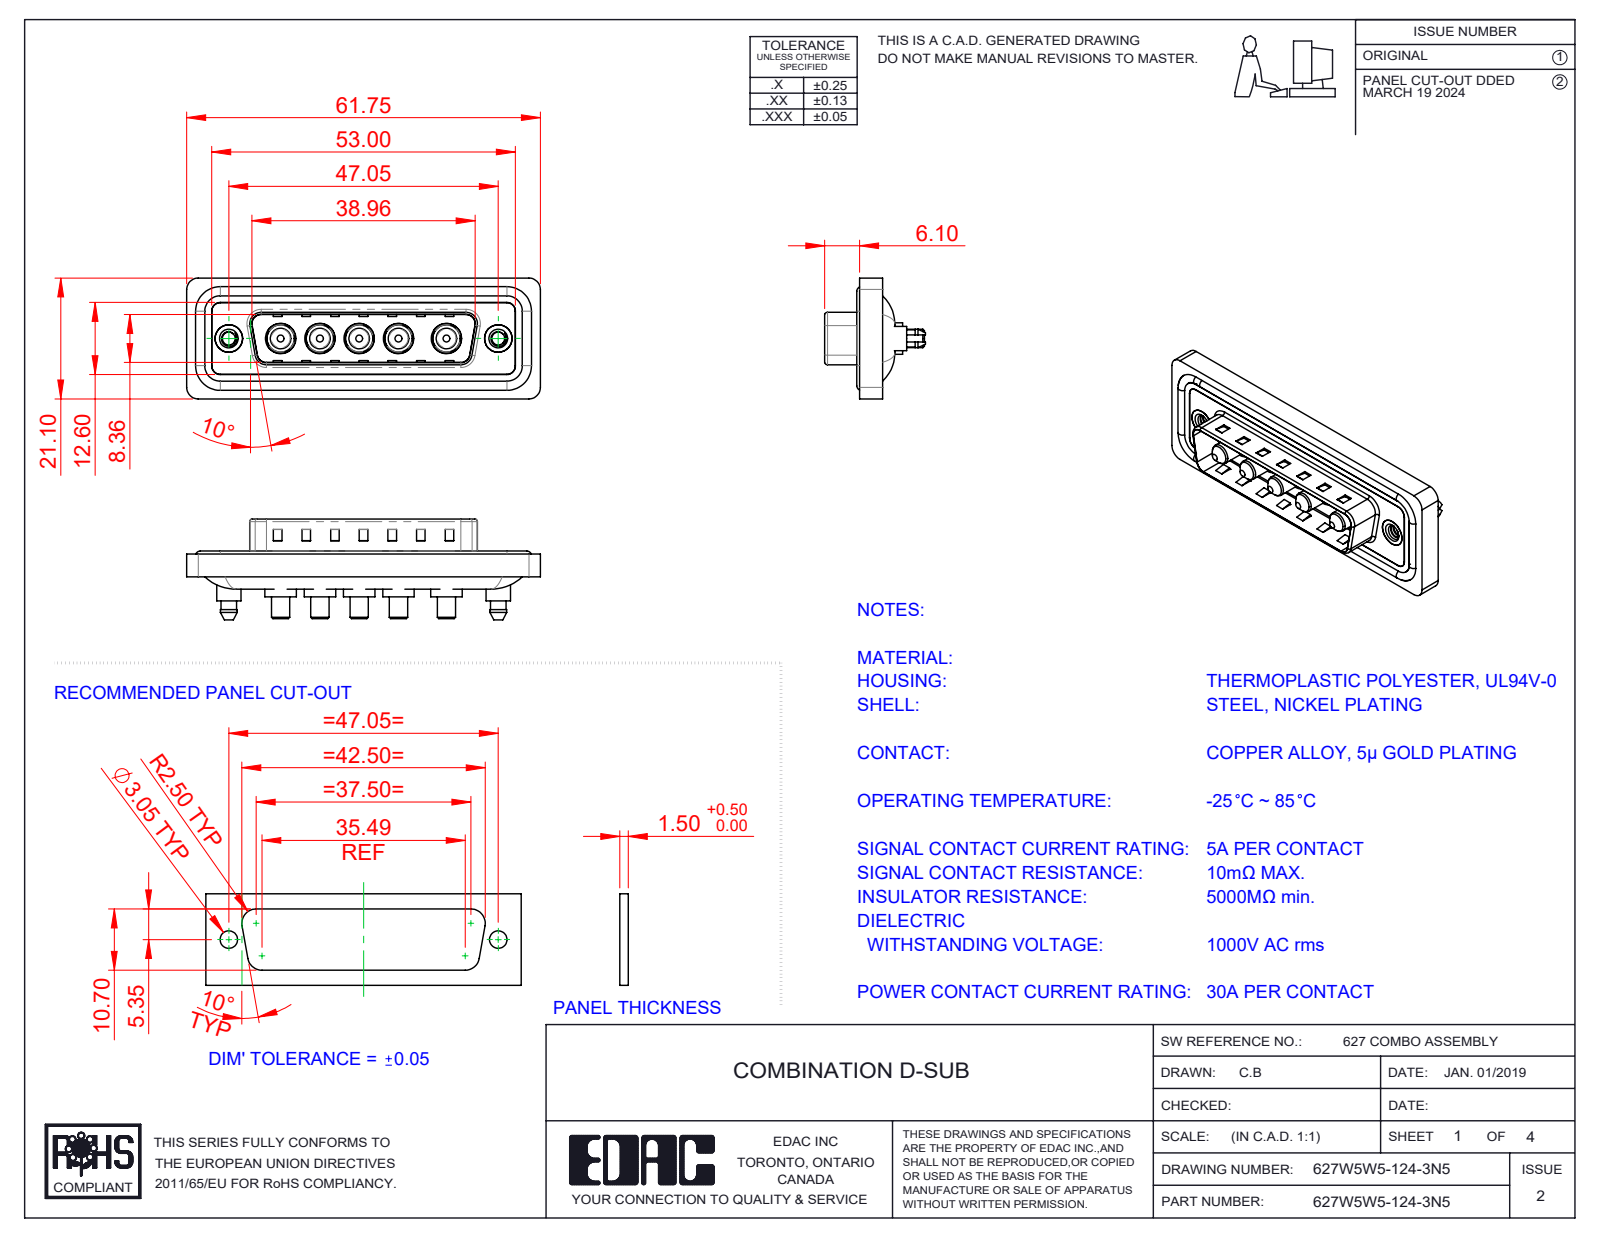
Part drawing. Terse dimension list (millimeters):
name: 627Combo Threaded Boardlock_5; Power Pin_30A S; 627Combo Shell Front_25 Contacts; 627Combo Shell Rear_25 Contacts (+3 more)
written by: SolidWorks 2023 (CONFIG_CONTROL_DESIGN)
unit: mm
bodies: 17 solids, 728 faces (275 planar, 315 cylindrical, 138 other)
size: 61.75 × 21.1 × 17.6
volume: 7 642 mm³; area: 12 152 mm²
holes: 5× ⌀4.85, 5× ⌀5.3, 2× ⌀2.26, 2× ⌀4, 2× ⌀4.8, 2× ⌀5
bosses: 5× ⌀5.5, 5× ⌀5.2, 5× ⌀4.75, 5× ⌀3.75, 5× ⌀3.6, 5× ⌀3.2, 4× ⌀1.6, 2× ⌀5.4
rounds: 24× R1.5, 18× R2, 10× R1.6, 8× R0.5, 5× R2.1, 4× R0.25, 4× R0.6, 4× R0.65
face distances: 0.4, 1.5, 3.1, 1.1, 0.5, 1.6, 2.9, 0.82, 9.58, 5.65
hole spacings: 6.86, 9.04, 13.73, 38.01, 6.87, 8.37, 8.38, 9.05
